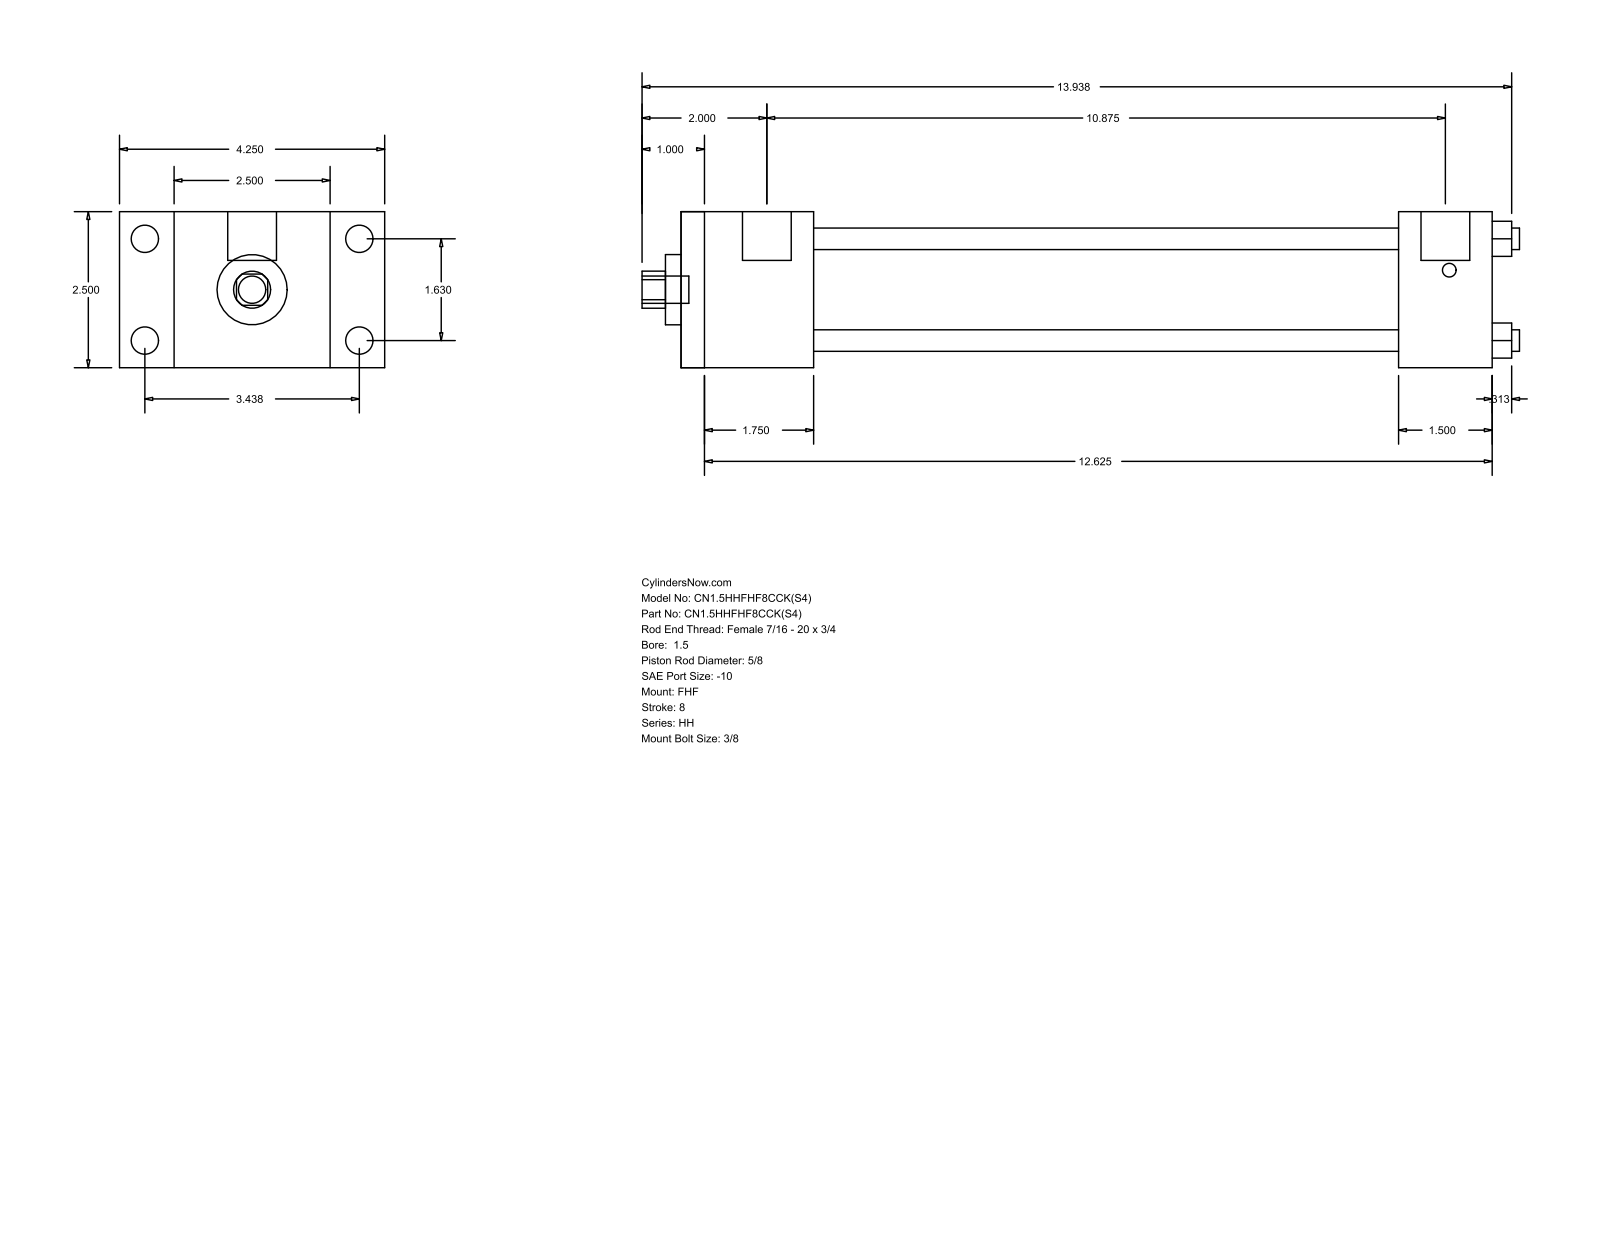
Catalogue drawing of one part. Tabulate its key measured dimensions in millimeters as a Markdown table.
| quantity | value |
| --- | --- |
| part name | HH_FHF__0150_0.625 |
| STEP written by | GSSL Pune (CONFIG_CONTROL_DESIGN) |
| units | millimeters |
| bodies | 0 solids, 88 faces (60 planar, 28 cylindrical, 0 other) |
| overall size | 357.19 × 107.95 × 63.5 |
| round holes (diameter × count) | 8.76 × 4, 15.88 × 1, 28.57 × 1, 44.45 × 1 |
| round bosses / shafts (diameter × count) | 11.13 × 4, 5.56 × 4, 19.84 × 2, 11.11 × 1 |
| partial cylindrical surfaces (radius × count) | 7.54 × 1 |
| main face-to-face distances | 63.5, 22.23, 85.73, 53.97, 107.96, 330.19, 276.22, 292.1, 238.13, 38.09 |
| hole center spacings | 29.27, 41.4, 58.55 |
